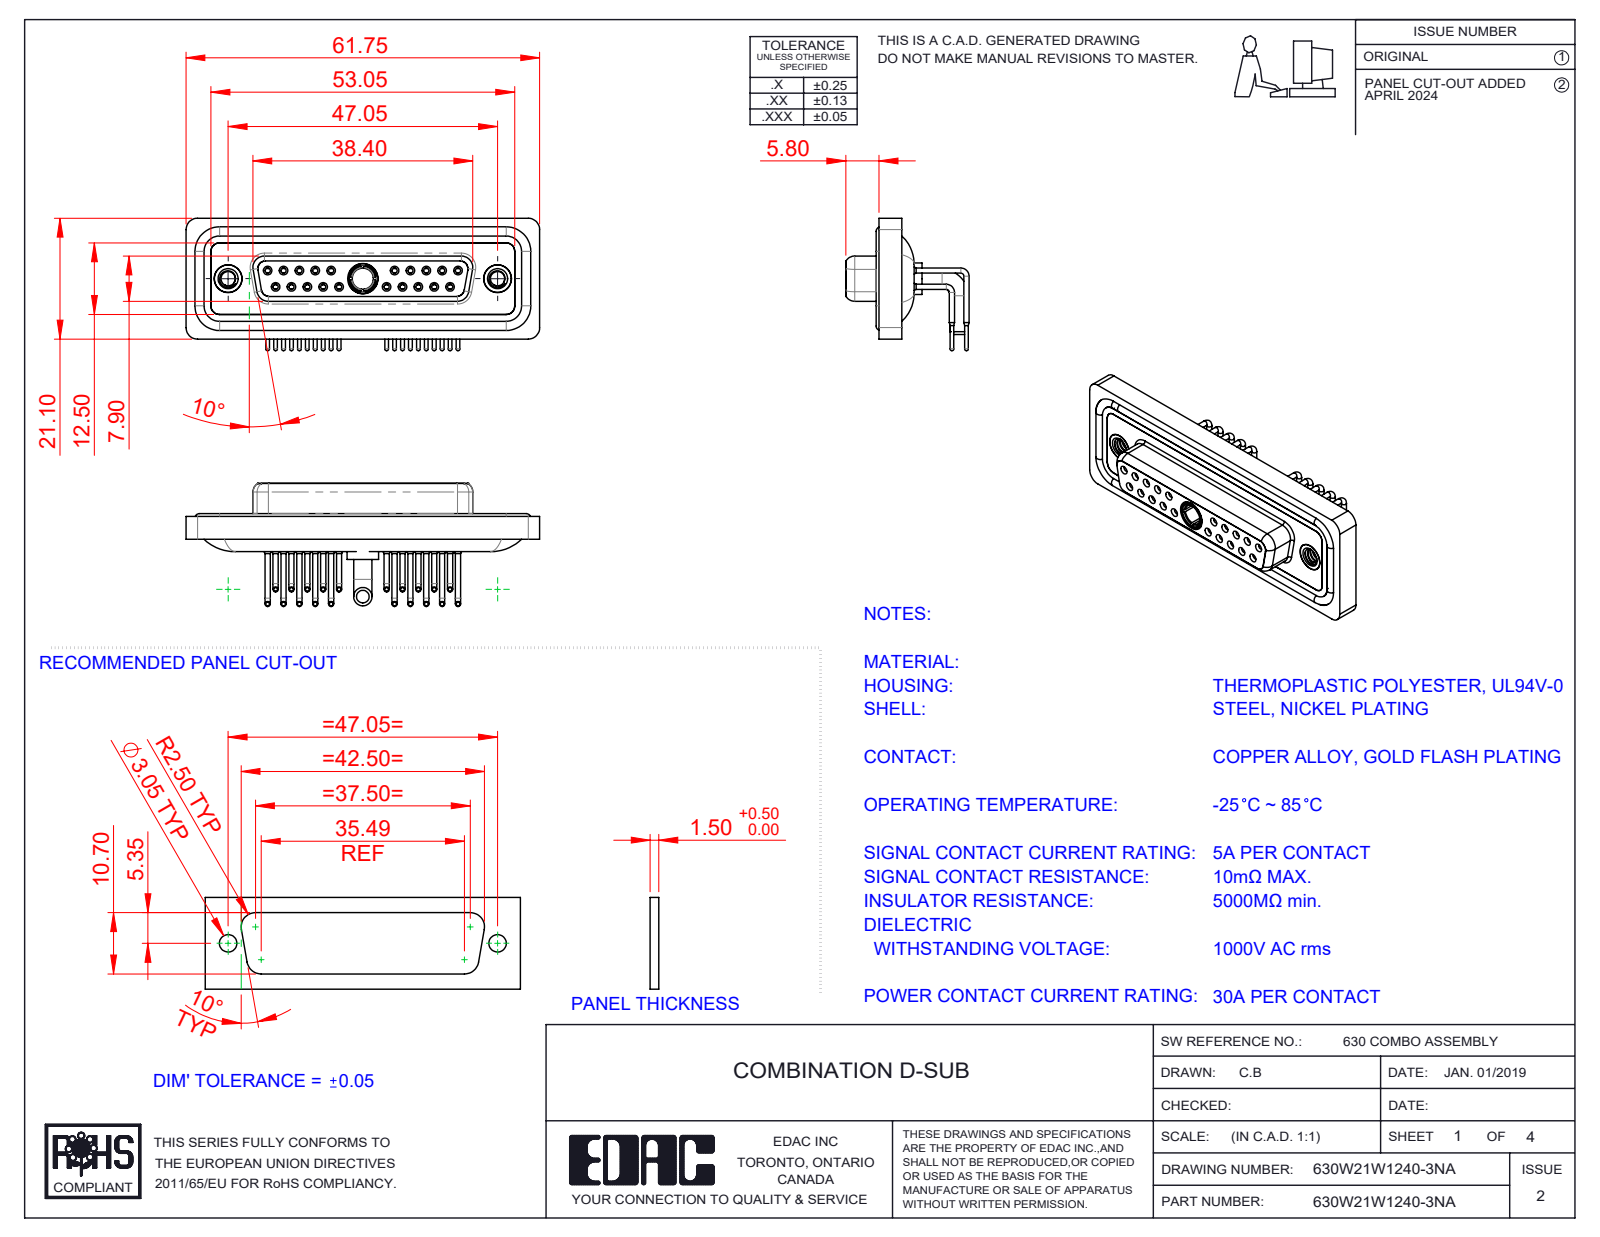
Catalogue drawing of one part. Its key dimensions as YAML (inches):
part_name: "630Combo Waterproof Housing_25 Contacts; 630W21W1140-3NA; 630Combo Shell Front_25 Contacts; 630Combo Contact Row 2_50 Contacts (+5 more)"
step_written_by: "SolidWorks 2023 (CONFIG_CONTROL_DESIGN)"
units: inches
bodies: {solids: 29, faces: 1518, planar: 434, cylindrical: 671, other: 413}
overall_size: [2.431, 0.91, 0.848]
volume: 0.52
surface_area: 22.94
round_holes:
  - {diameter: 0.035, count: 20}
  - {diameter: 0.043, count: 20}
  - {diameter: 0.059, count: 20}
  - {diameter: 0.079, count: 20}
  - {diameter: 0.063, count: 10}
  - {diameter: 0.067, count: 10}
  - {diameter: 0.191, count: 3}
  - {diameter: 0.098, count: 2}
  - {diameter: 0.157, count: 2}
  - {diameter: 0.159, count: 2}
  - {diameter: 0.197, count: 2}
  - {diameter: 0.146, count: 1}
round_bosses_or_shafts:
  - {diameter: 0.035, count: 20}
  - {diameter: 0.026, count: 20}
  - {diameter: 0.063, count: 14}
  - {diameter: 0.195, count: 2}
  - {diameter: 0.189, count: 2}
  - {diameter: 0.126, count: 2}
  - {diameter: 0.217, count: 1}
  - {diameter: 0.205, count: 1}
partial_cylinders:
  - {radius: 0.059, count: 18}
  - {radius: 0.079, count: 18}
  - {radius: 0.053, count: 8}
  - {radius: 0.063, count: 8}
  - {radius: 0.01, count: 4}
  - {radius: 0.02, count: 4}
  - {radius: 0.024, count: 4}
  - {radius: 0.026, count: 4}
face_to_face_distances: [0.016, 0.071, 0.161, 0.063, 0.043, 0.098, 0.122, 0.059, 0.386, 0.018]
hole_center_spacings: [0.124, 0.109, 0.218, 0.327, 0.198, 0.763, 0.826, 0.872]
